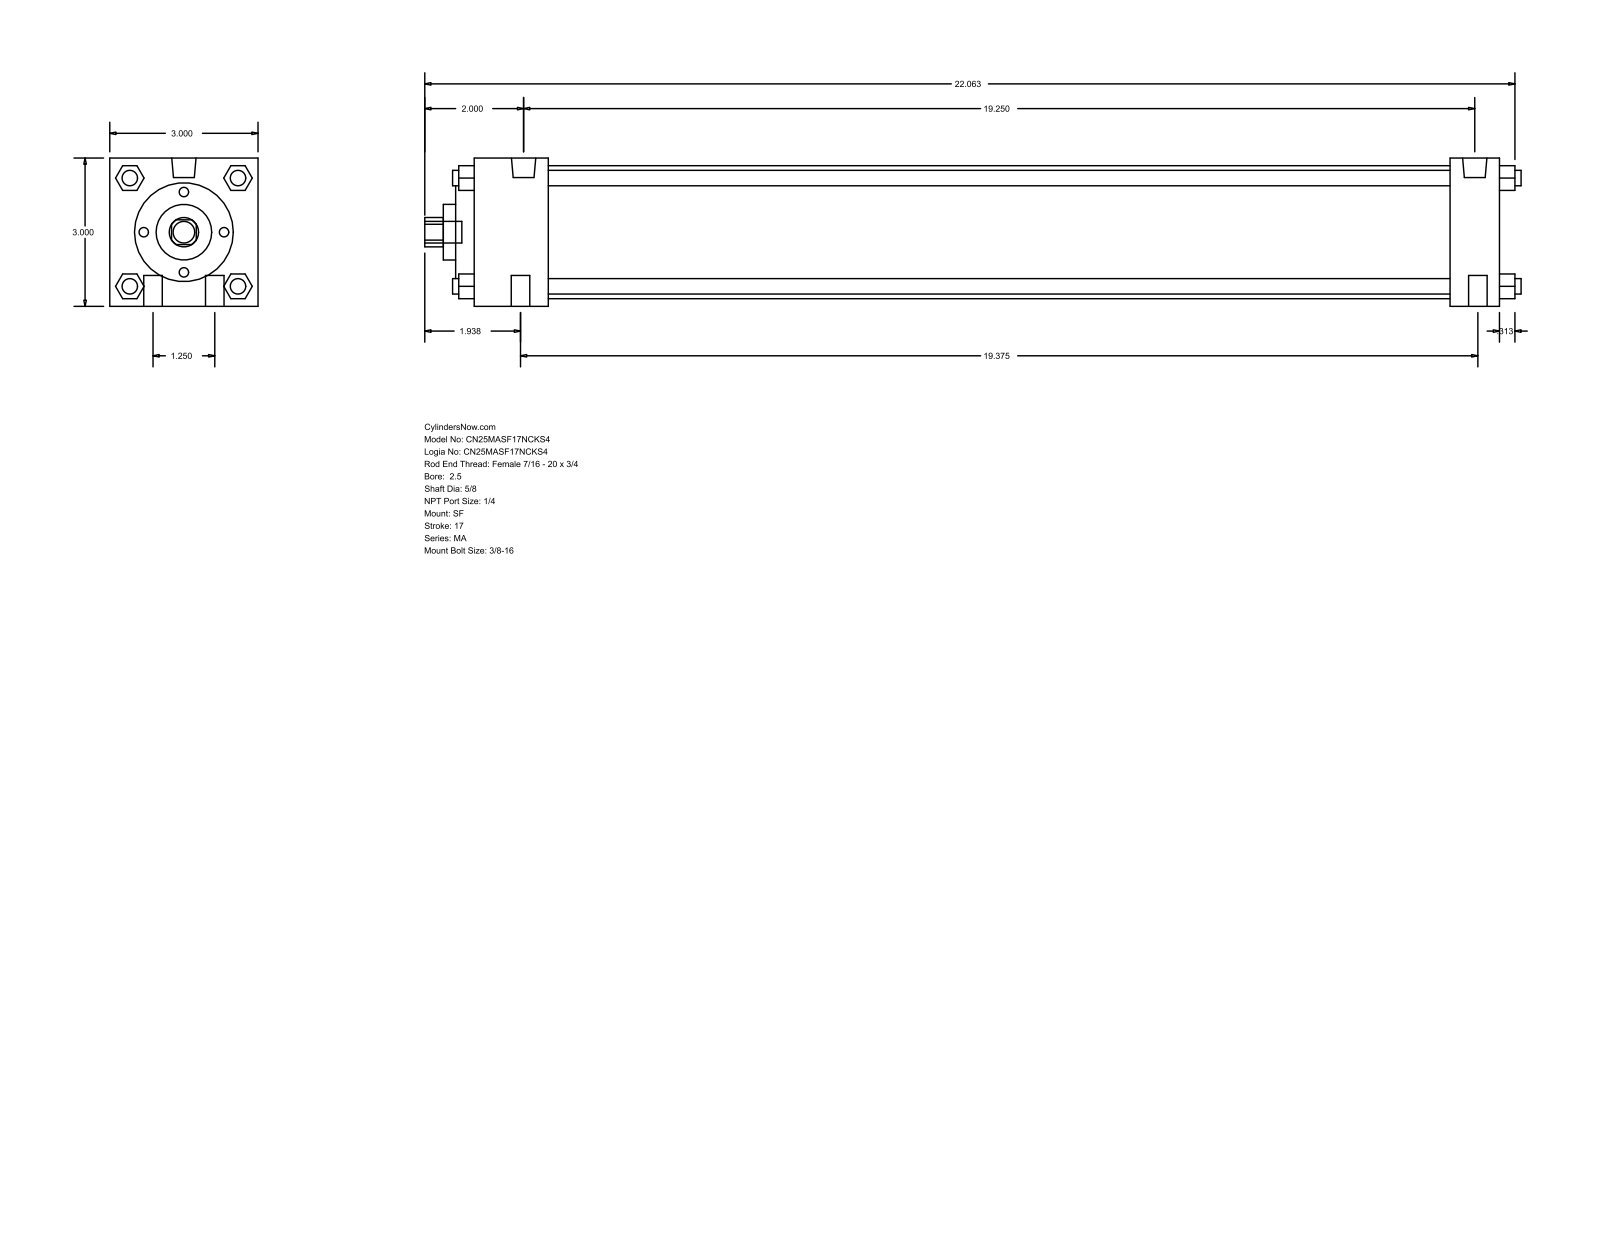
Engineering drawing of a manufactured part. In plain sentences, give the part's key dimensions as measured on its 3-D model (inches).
The part is named "MA_SF__0250_0.625". Its 3-D file was written by "GSSL Pune (CONFIG_CONTROL_DESIGN)". It is 0 solids with 126 faces: 95 planar, 31 cylindrical and 0 other. Overall it measures 22.187 by 3 by 3 inches. Round holes: 1 of diameter 0.625, 1 of diameter 1.125, 1 of diameter 2, 1 of diameter 2.69. Round bosses or shafts: 6 of diameter 0.313, 4 of diameter 0.375, 2 of diameter 0.492, 1 of diameter 0.437. Partial cylindrical surfaces (rounded edges, fillets, slot ends): 1 of radius 0.297. The main face-to-face distances are 3, 20.75, 1, 19.75, 1.5, 18.25, 19.25, 0.5, 0.375, 1.875.
